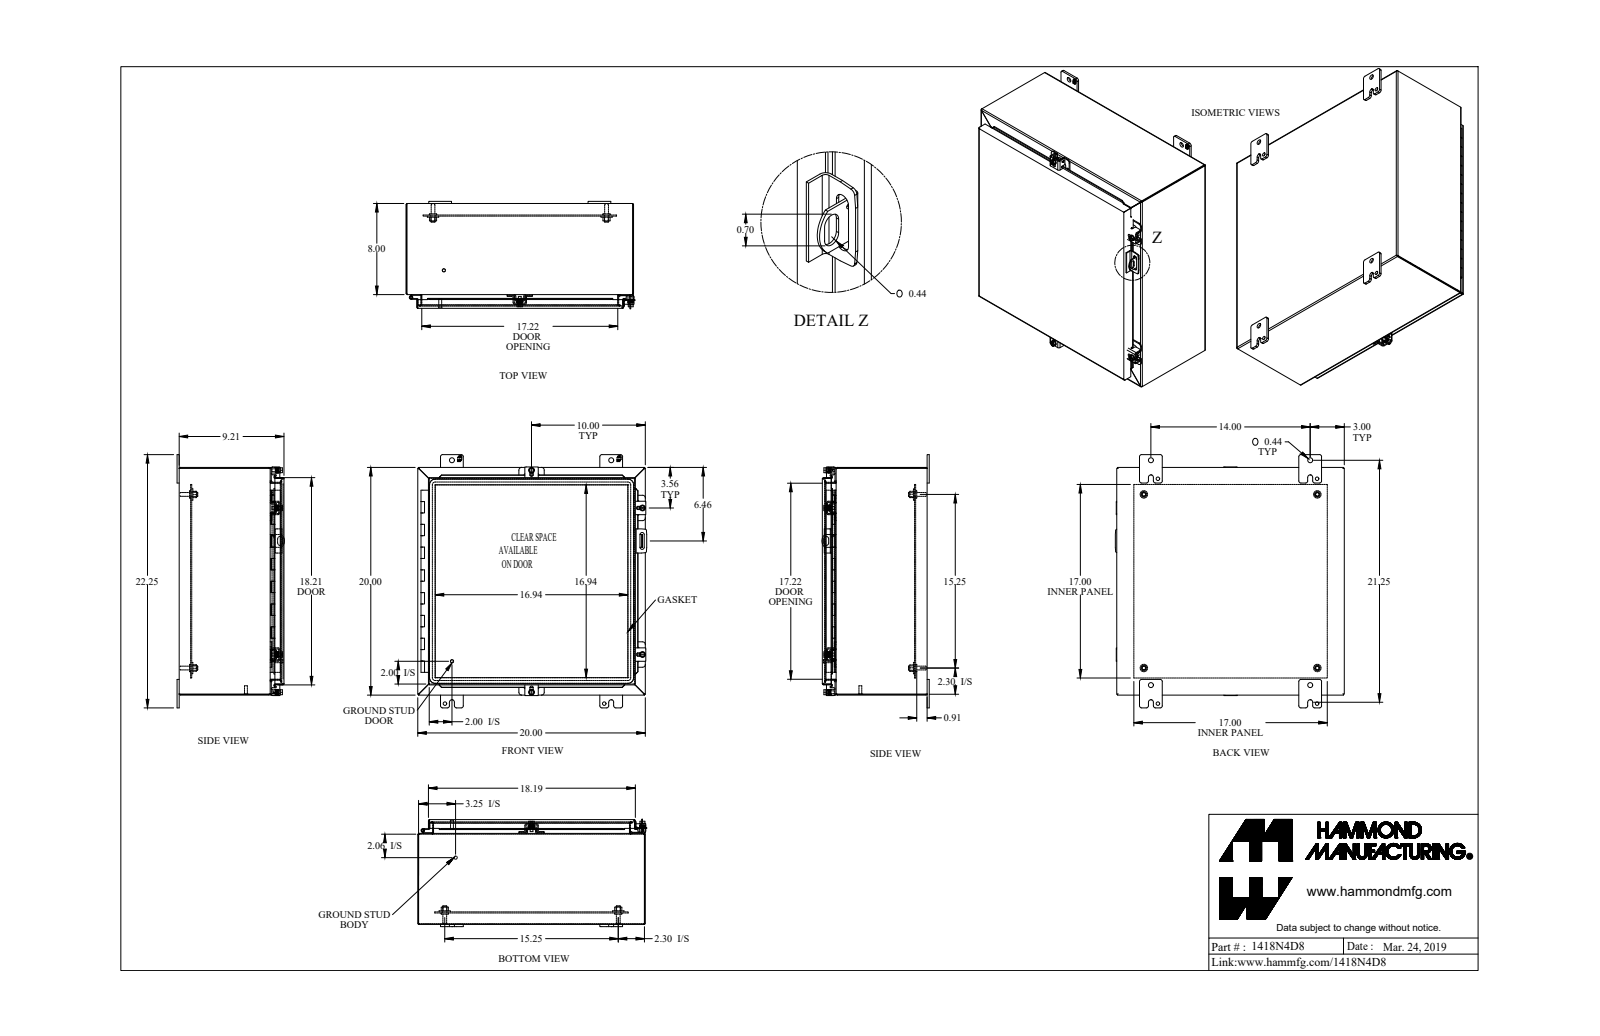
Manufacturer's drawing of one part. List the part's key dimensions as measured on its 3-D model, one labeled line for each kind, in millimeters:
Part name (STEP PRODUCT): 1418N4D8_Default
STEP written by: SolidWorks 2019 (CONFIG_CONTROL_DESIGN)
Units: millimetres
Bodies: 39 solids, 1368 faces (833 planar, 451 cylindrical, 84 other)
Overall size (bounding box): 565.2 × 511.2 × 239.7
Volume: 2 591 000 mm³ · Surface area: 2 683 000 mm²
Round holes (diameter × count): ⌀5.4 ×4, ⌀6.7 ×4, ⌀8 ×4, ⌀9.5 ×4, ⌀11.1 ×4, ⌀12.7 ×4, ⌀7.8 ×2, ⌀11.3 ×2, ⌀3.2 ×1, ⌀4.7 ×1
Round bosses / shafts (diameter × count): ⌀16.5 ×4, ⌀12.7 ×4, ⌀9.9 ×4, ⌀9.5 ×4, ⌀8.4 ×4, ⌀6.2 ×4, ⌀25.4 ×2, ⌀7.1 ×2
Partial cylindrical surfaces — rounded edges, fillets, slot ends (radius × count): R4.8 ×26, R0.9 ×24, R2.7 ×24, R1.2 ×21, R3.6 ×21, R6.4 ×20, R1.1 ×8, R3.2 ×8
Main face-to-face distances: 1.8, 506.2, 230.3, 232.1, 1.8, 232.1, 233.9, 504.3, 508, 2.4
Hole centre spacings: 387.4, 481.9, 547.8, 201.1, 355.6, 61.8, 201, 387.4
